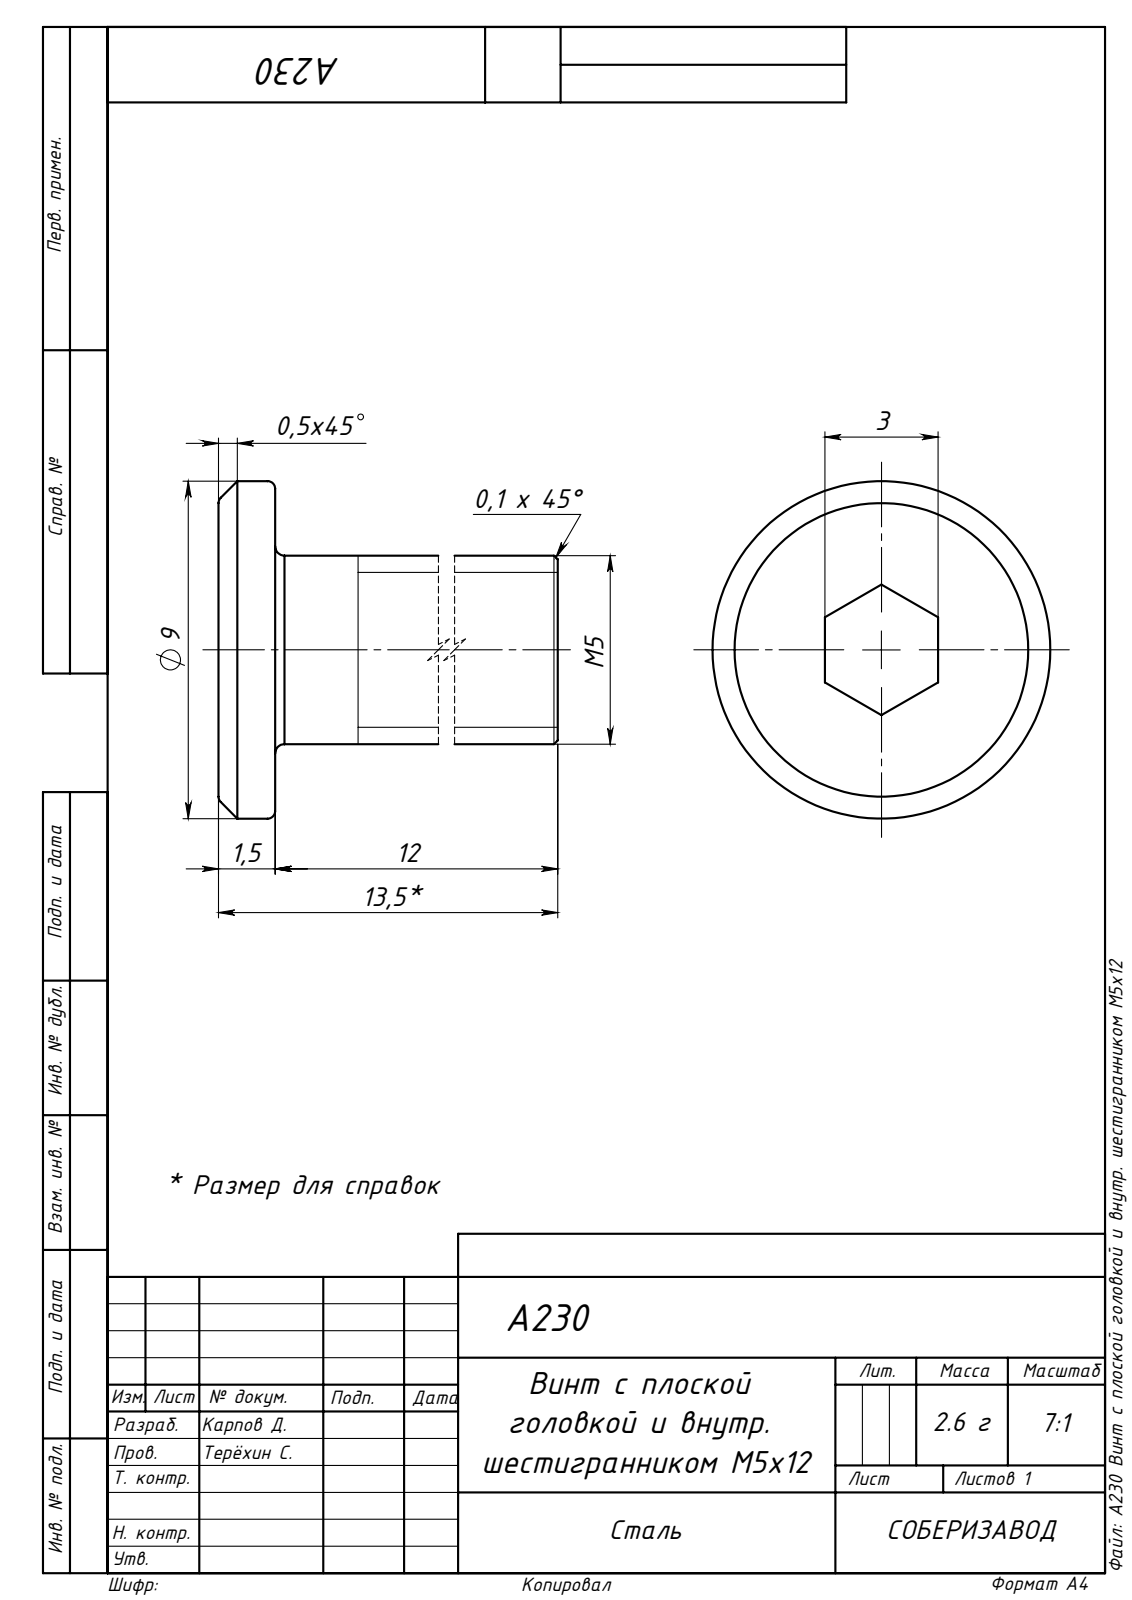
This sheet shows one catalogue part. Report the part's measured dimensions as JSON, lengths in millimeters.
{"step_written_by": "SolidWorks 2020 (AUTOMOTIVE_DESIGN)", "units": "millimeters", "bodies": {"solids": 1, "faces": 24, "planar": 10, "cylindrical": 4, "other": 10}, "overall_size": [13.5, 8.95, 8.95], "volume_mm3": 321, "surface_area_mm2": 350, "round_bosses_or_shafts": [[8.95, 1], [5, 1]], "face_to_face_distances": [1.5, 12, 13.5, 0.75, 12.75, 3]}
